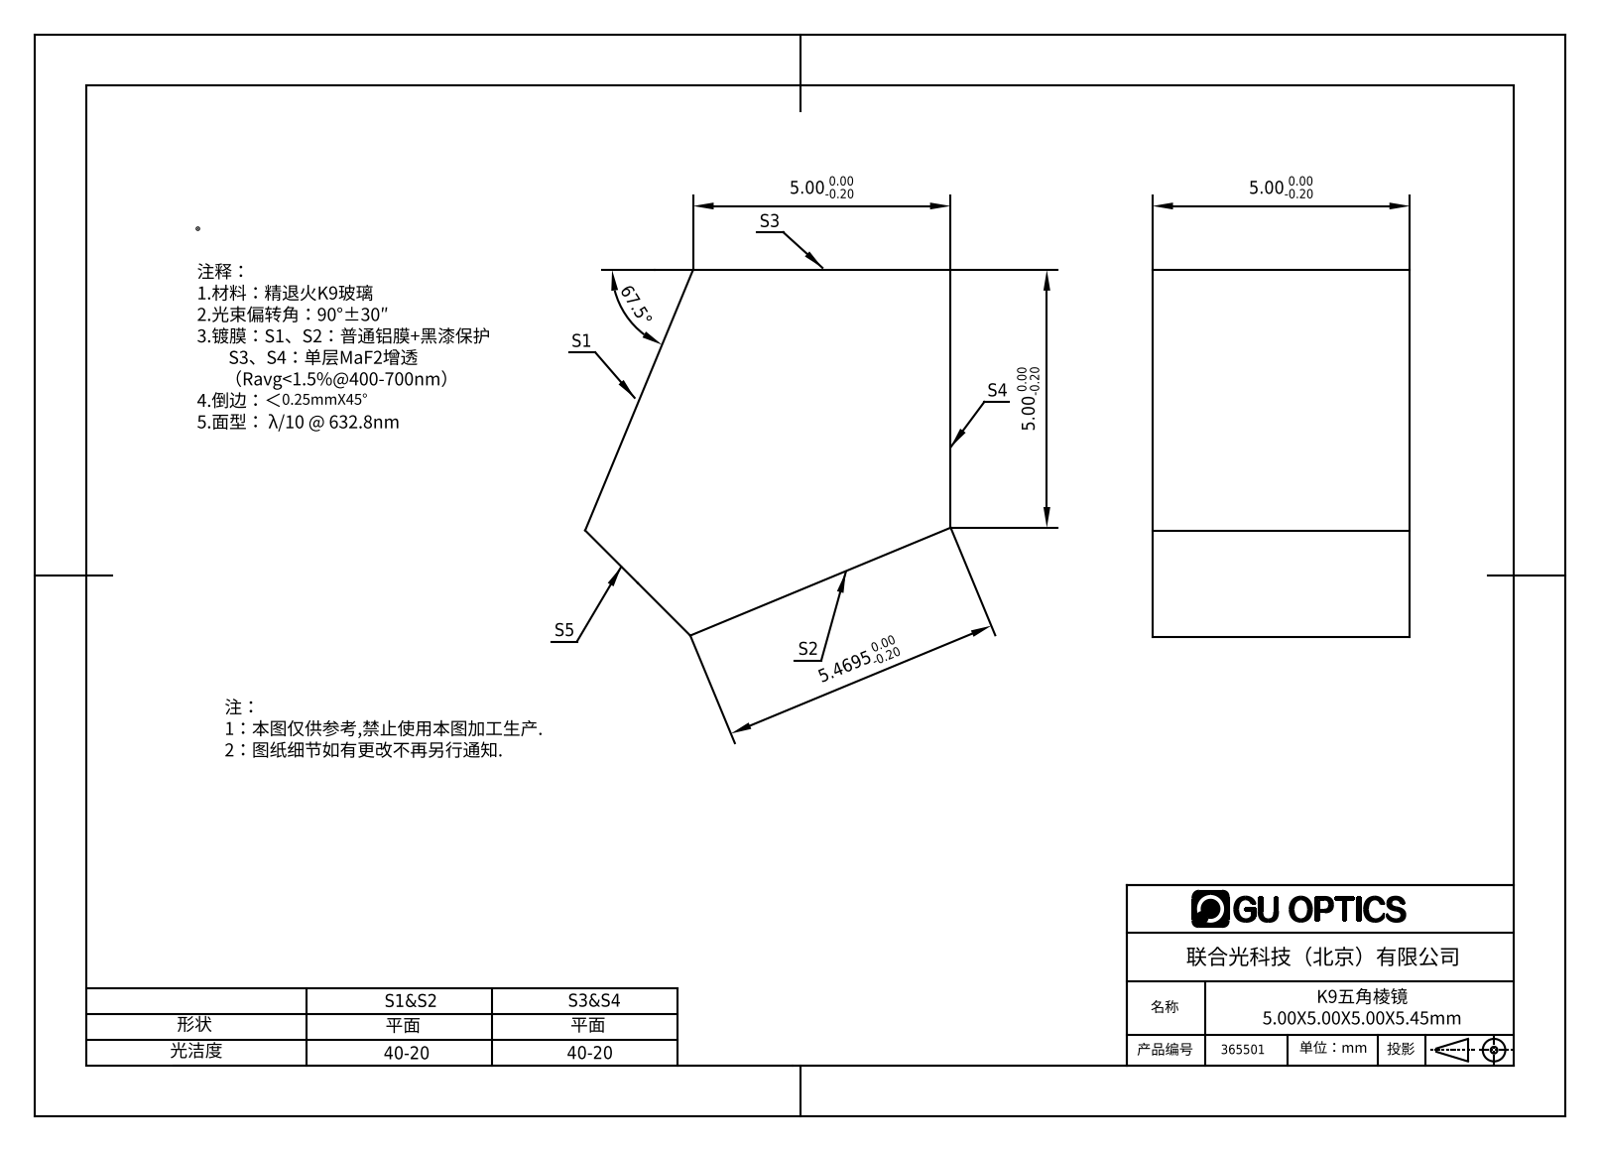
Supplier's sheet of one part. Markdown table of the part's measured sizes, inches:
| quantity | value |
| --- | --- |
| part name | 365500 |
| STEP written by | SolidWorks 2016 (CONFIG_CONTROL_DESIGN) |
| units | inches |
| bodies | 1 solid, 7 faces (7 planar, 0 cylindrical, 0 other) |
| overall size | 0.281 × 0.28 × 0.197 |
| volume | 0.012 in³ |
| surface area | 0.302 in² |
| main face-to-face distances | 0.197 |
